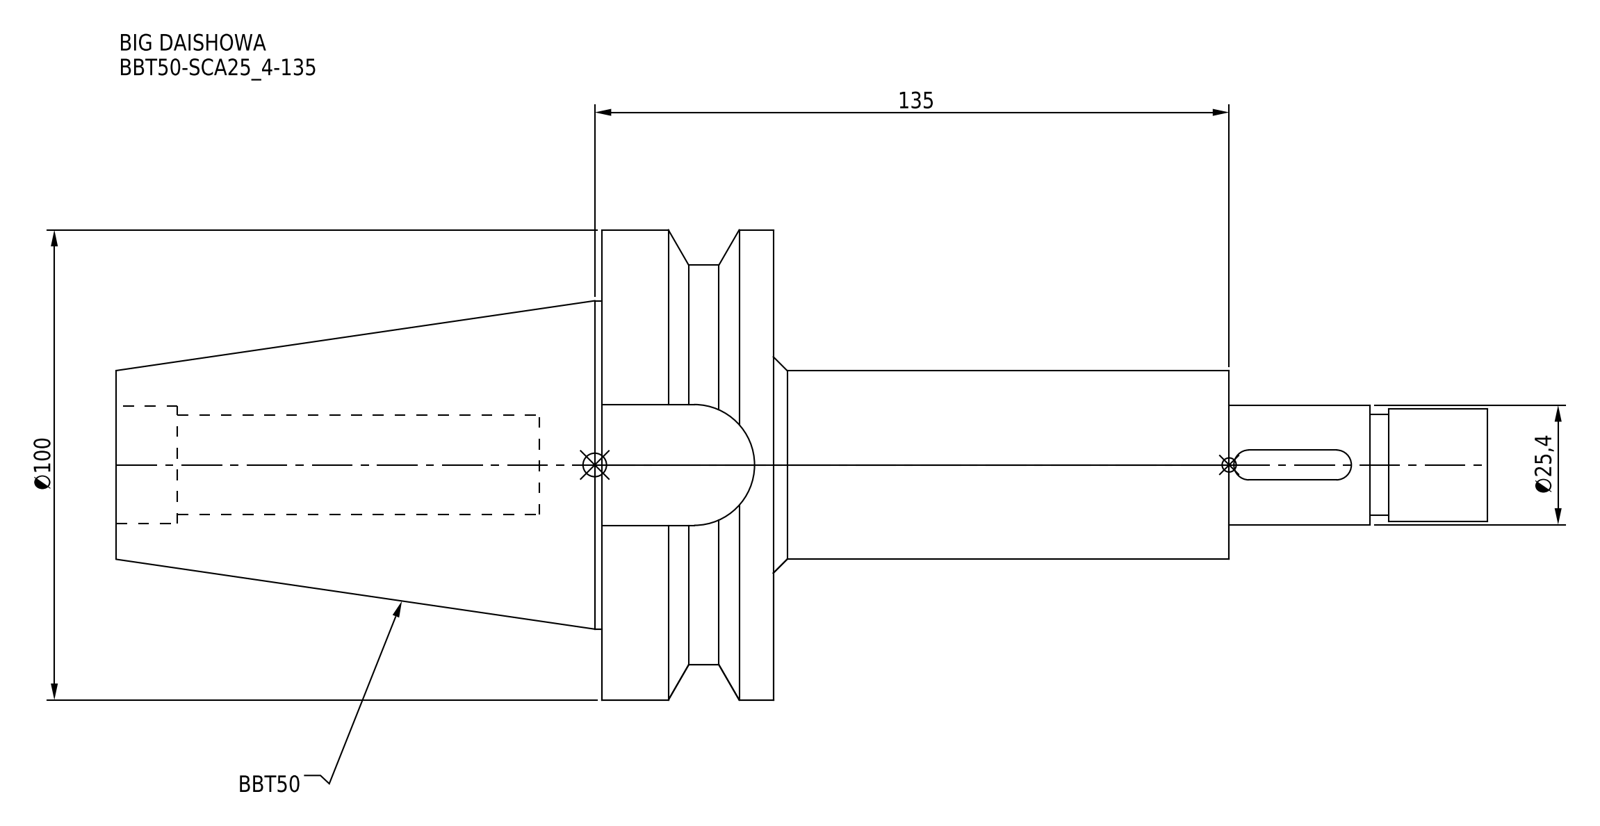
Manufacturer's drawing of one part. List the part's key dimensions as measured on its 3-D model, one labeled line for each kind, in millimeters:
Part name (STEP PRODUCT): BBT50-SCA25_4-135
STEP written by: CREO PARAMETRIC BY PTC INC, 2016380 (AUTOMOTIVE_DESIGN)
Units: millimetres
Bodies: 1 solid, 42 faces (12 planar, 22 cylindrical, 8 other)
Overall size (bounding box): 291.8 × 100 × 100
Volume: 631 962 mm³ · Surface area: 67 431 mm²
Round holes (diameter × count): ⌀21.2 ×1, ⌀25 ×1
Round bosses / shafts (diameter × count): ⌀100 ×1, ⌀85 ×1, ⌀69.85 ×1, ⌀40 ×1, ⌀25.4 ×1, ⌀24 ×1, ⌀21.5 ×1
Partial cylindrical surfaces — rounded edges, fillets, slot ends (radius × count): R3.17 ×2
Main face-to-face distances: 36.5, 139.8, 103.3, 97, 133.5, 236.8, 55, 152, 188.5, 291.8
